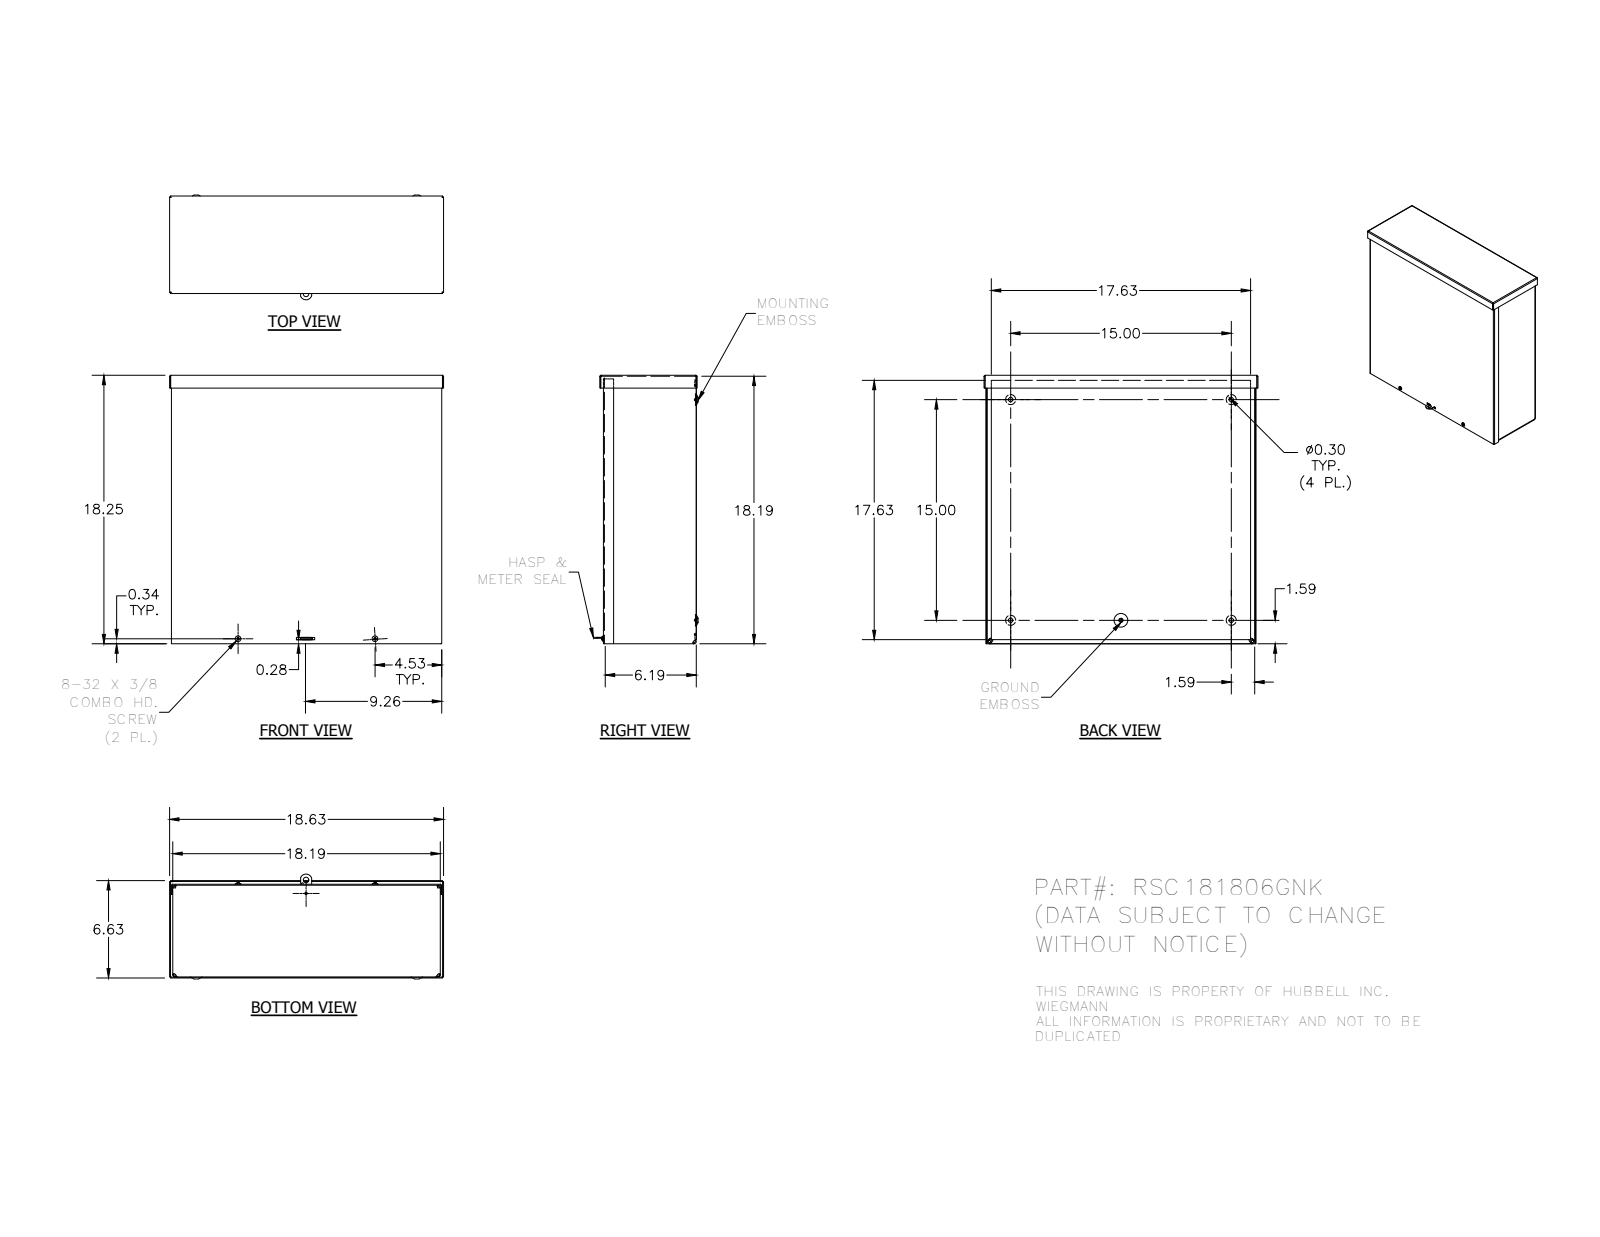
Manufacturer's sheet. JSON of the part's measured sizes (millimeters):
{"part_name": "RSC181806GNK_WRAP; RSC1818GNK_LID; RSC1806GNK_CAP; 3183 (+3 more)", "step_written_by": "Autodesk Inventor 2014 (AUTOMOTIVE_DESIGN)", "units": "millimeters", "bodies": {"solids": 7, "faces": 377, "planar": 163, "cylindrical": 78, "other": 136}, "overall_size": [473.07, 463.56, 180.97], "volume_mm3": 1402000, "surface_area_mm2": 1793000, "round_holes": [[7.62, 4], [7.95, 4], [3.17, 2], [3.76, 2], [3.96, 1], [4.19, 1], [9.52, 1]], "round_bosses_or_shafts": [[9.75, 2], [4.17, 2], [5.8, 1]], "partial_cylinders_radius": [[0.79, 8], [2.37, 8], [3.17, 8], [4.75, 8], [1.4, 4], [1.57, 4], [2.38, 4], [2.97, 4]], "face_to_face_distances": [1.58, 460.39, 158.73, 157.15, 1.59, 160.32, 158.74, 1.57, 461.97, 3.15], "hole_center_spacings": [381, 190.5, 236.55, 419.05, 424.74, 425.96, 439.73, 499.32]}
